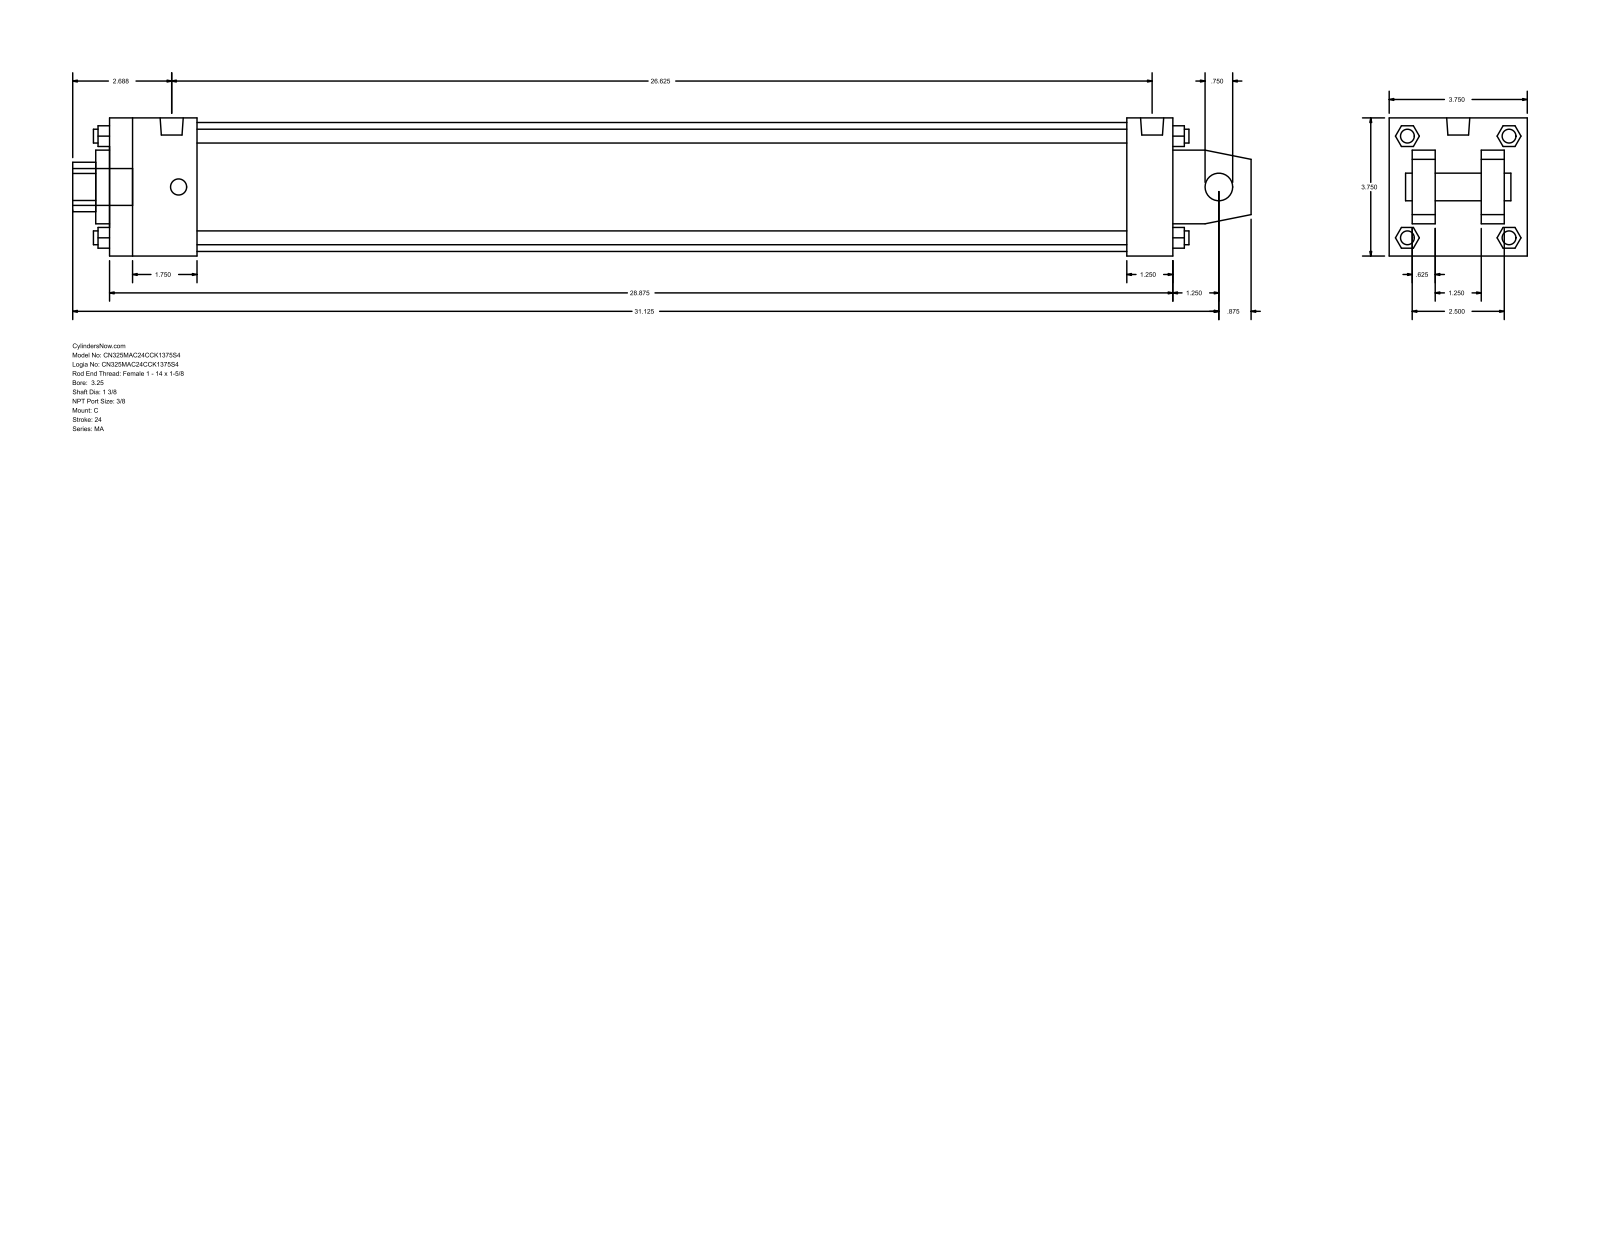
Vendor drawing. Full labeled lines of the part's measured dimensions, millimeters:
Part name (STEP PRODUCT): MA_C__0325_1.375
STEP written by: GSSL Pune (CONFIG_CONTROL_DESIGN)
Units: millimetres
Bodies: 0 solids, 139 faces (108 planar, 31 cylindrical, 0 other)
Overall size (bounding box): 812.8 × 95.25 × 95.25
Round holes (diameter × count): ⌀19.05 ×1, ⌀34.92 ×1, ⌀50.8 ×1, ⌀88.9 ×1
Round bosses / shafts (diameter × count): ⌀11.11 ×4, ⌀9.53 ×4, ⌀15.93 ×2, ⌀25.4 ×1
Partial cylindrical surfaces — rounded edges, fillets, slot ends (radius × count): R17.06 ×1
Main face-to-face distances: 95.24, 15.87, 63.5, 733.43, 31.74, 79.37, 47.63, 701.68, 31.75, 60.32
